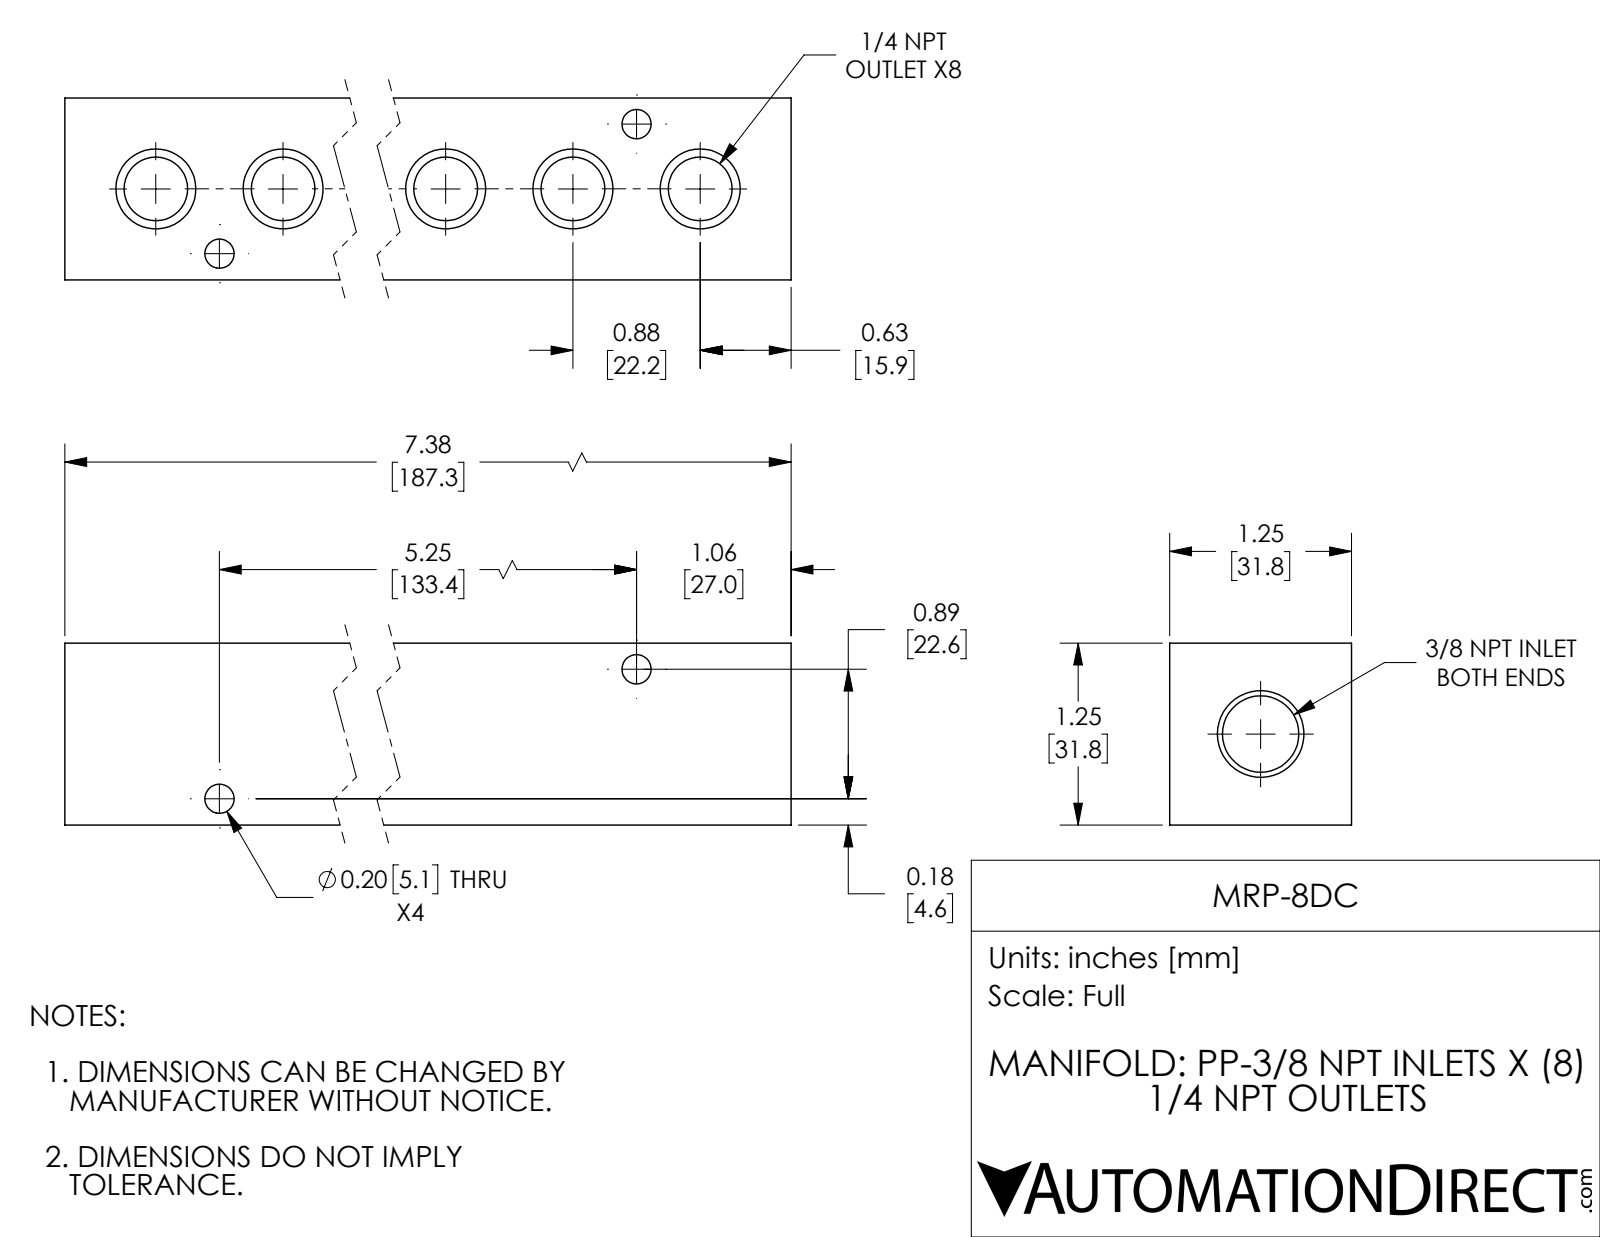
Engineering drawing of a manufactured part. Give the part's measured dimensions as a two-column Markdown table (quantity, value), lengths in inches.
| quantity | value |
| --- | --- |
| part name | MRP-8DC |
| STEP written by | SolidWorks 2018 (AUTOMOTIVE_DESIGN) |
| units | inches |
| bodies | 1 solid, 60 faces (6 planar, 34 cylindrical, 20 other) |
| overall size | 7.375 × 1.25 × 1.25 |
| volume | 9.291 in³ |
| surface area | 55.95 in² |
| round holes (diameter × count) | 0.438 × 8, 0.201 × 4, 0.525 × 1 |
| main face-to-face distances | 1.25, 7.375 |
| hole center spacings | 1.75, 0.624, 0.875, 0.875, 2.625, 3.5, 2.625, 4.375 |
